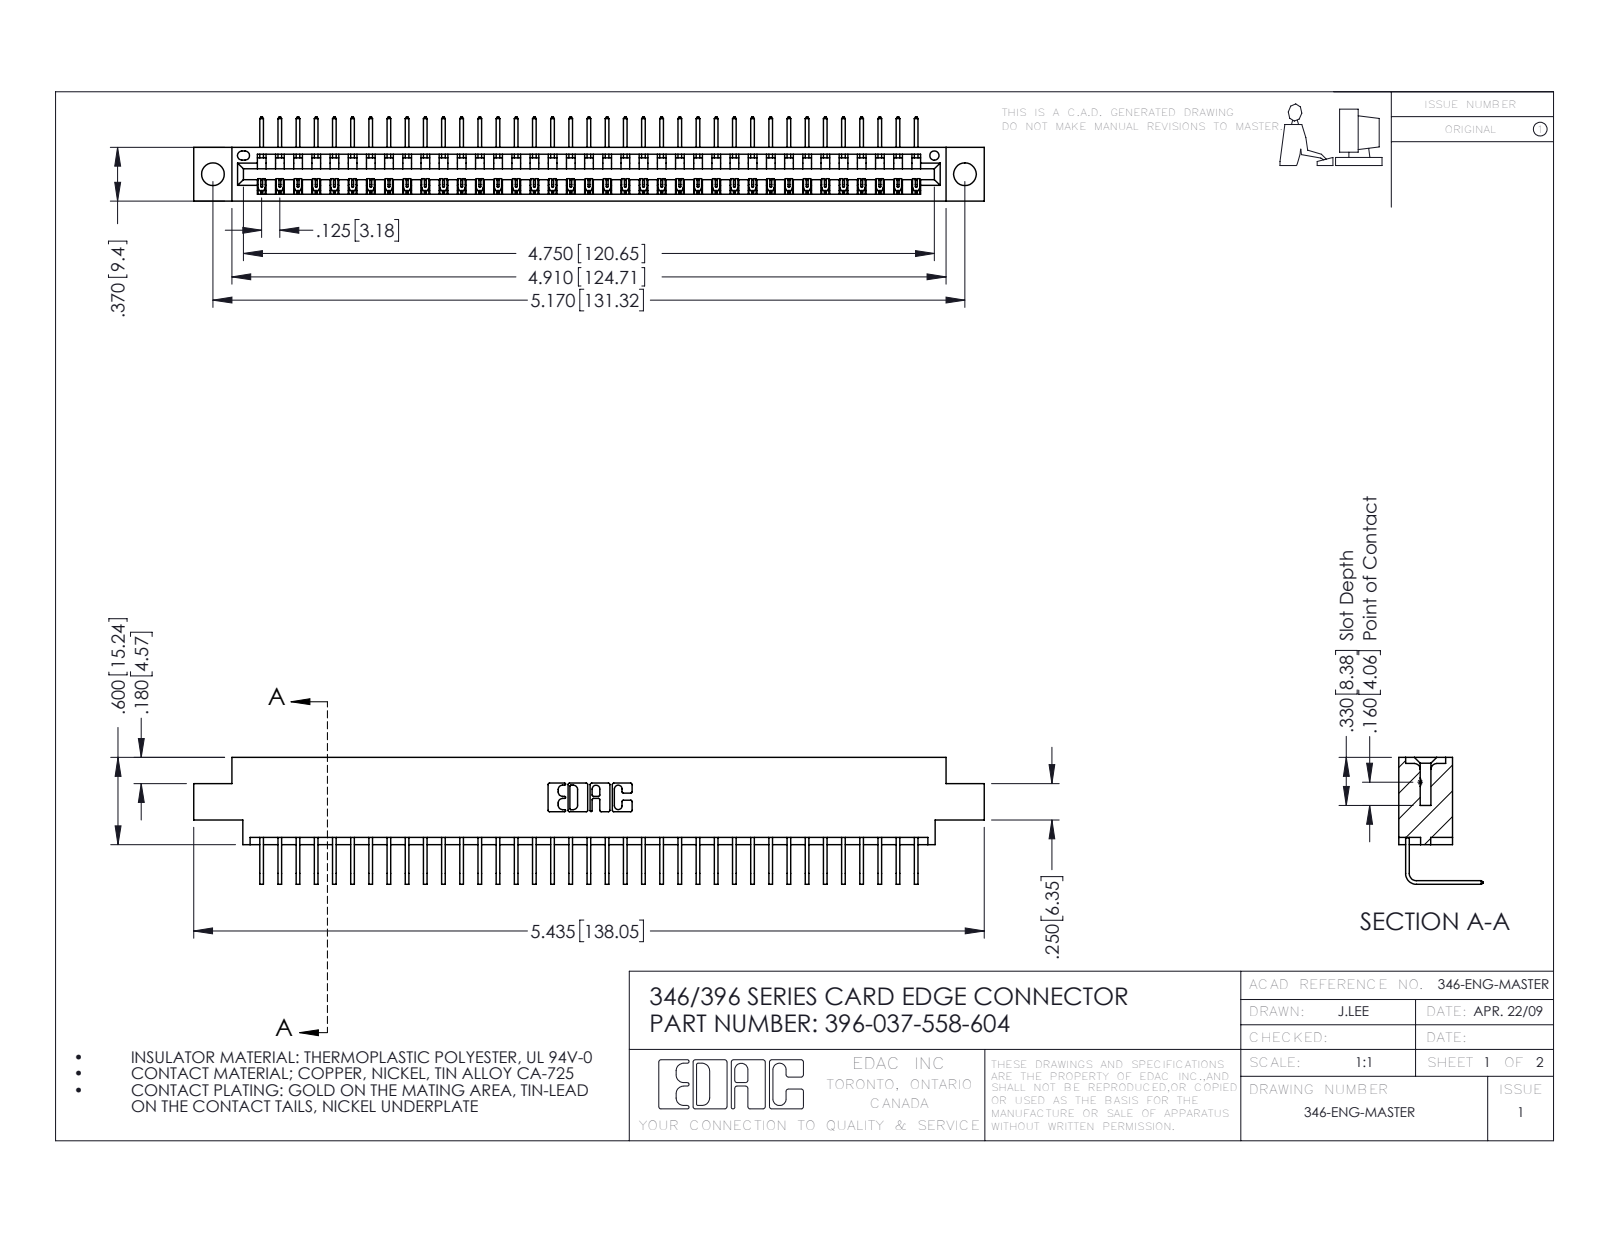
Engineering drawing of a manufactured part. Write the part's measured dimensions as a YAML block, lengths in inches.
part_name: "396-037-558-604; 345-292-001_558 Tail - 2; 346 Part_0.170 Offset - 0.156 Dia-TH"
step_written_by: "SolidWorks 2016 (CONFIG_CONTROL_DESIGN)"
units: inches
bodies: {solids: 38, faces: 2346, planar: 1634, cylindrical: 712, other: 0}
overall_size: [5.435, 0.873, 0.58]
volume: 0.797
surface_area: 26.31
round_holes:
  - {diameter: 0.156, count: 2}
  - {diameter: 0.064, count: 1}
partial_cylinders:
  - {radius: 0.006, count: 74}
  - {radius: 0.01, count: 22}
  - {radius: 0.007, count: 6}
  - {radius: 0.031, count: 6}
  - {radius: 0.026, count: 3}
  - {radius: 0.031, count: 2}
  - {radius: 0.04, count: 2}
  - {radius: 0.014, count: 1}
face_to_face_distances: [0.322, 0.048, 0.37, 0.25, 0.298, 0.025, 0.072, 0.148, 0.222, 0.1]
hole_center_spacings: [0.246, 4.961, 5.17]
